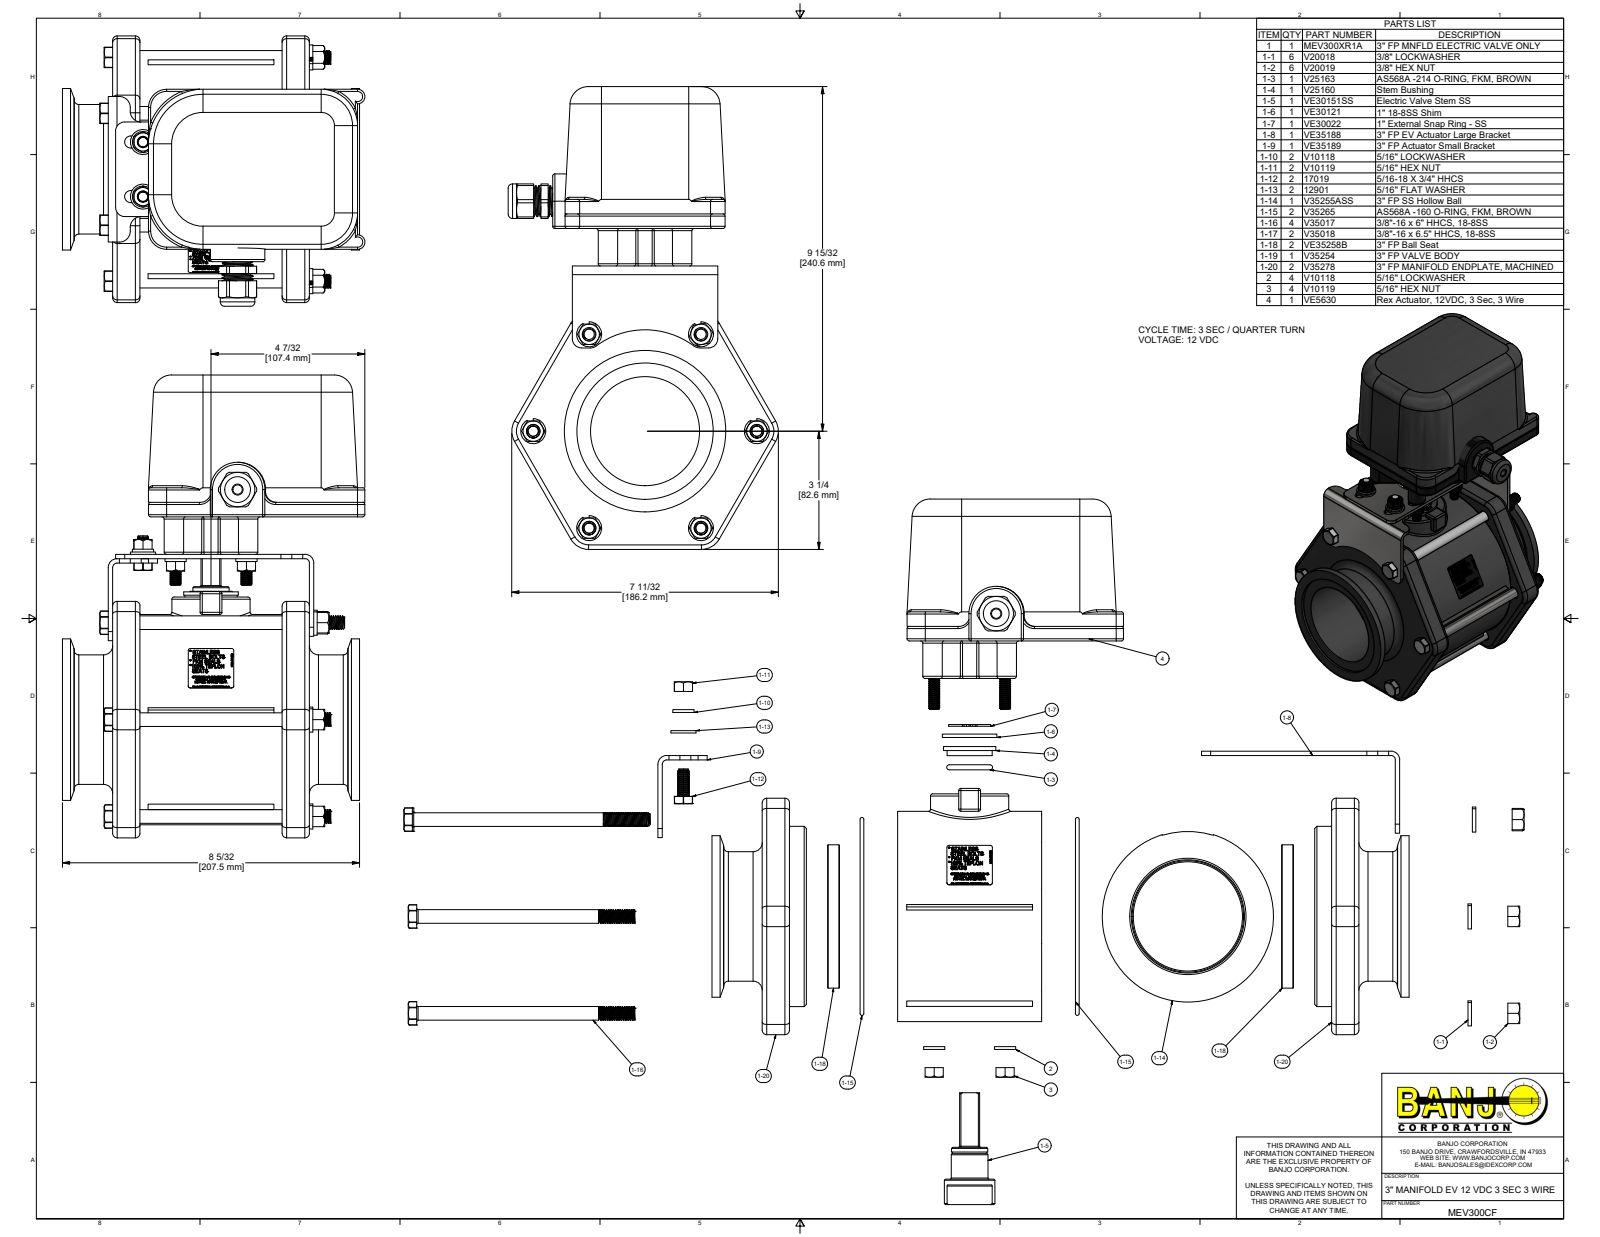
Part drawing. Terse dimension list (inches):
name: MEV300CF; MEV300XR1A; V35254; VL1000 (+8 more)
written by: Autodesk Inventor 2019 (AUTOMOTIVE_DESIGN)
unit: in
bodies: 81 solids, 5328 faces (2441 planar, 1347 cylindrical, 1540 other)
size: 12.722 × 8.315 × 7.431
volume: 154 in³; area: 1 116 in²
holes: 12× ⌀0.171, 8× ⌀0.052, 8× ⌀0.079, 6× ⌀0.047, 6× ⌀0.252, 6× ⌀0.307, 6× ⌀0.322, 6× ⌀0.385, 6× ⌀0.44, 5× ⌀0.25, 4× ⌀0.14, 4× ⌀0.19
bosses: 26× ⌀0.268, 7× ⌀0.375, 6× ⌀0.687, 6× ⌀0.583, 6× ⌀0.315, 4× ⌀0.325, 4× ⌀0.305, 4× ⌀0.25
rounds: 63× R0.06, 43× R0.035, 24× R0.125, 16× R0.3, 14× R0.03, 12× R0.25, 8× R0.172, 6× R0.32
face distances: 5.41, 0.725, 4.685, 0.12, 4.73, 0.22, 0.8, 4.61, 0.075, 3.885
hole spacings: 2.264, 2.805, 0.813, 3.075, 4.667, 5.418, 5.433, 1.693
